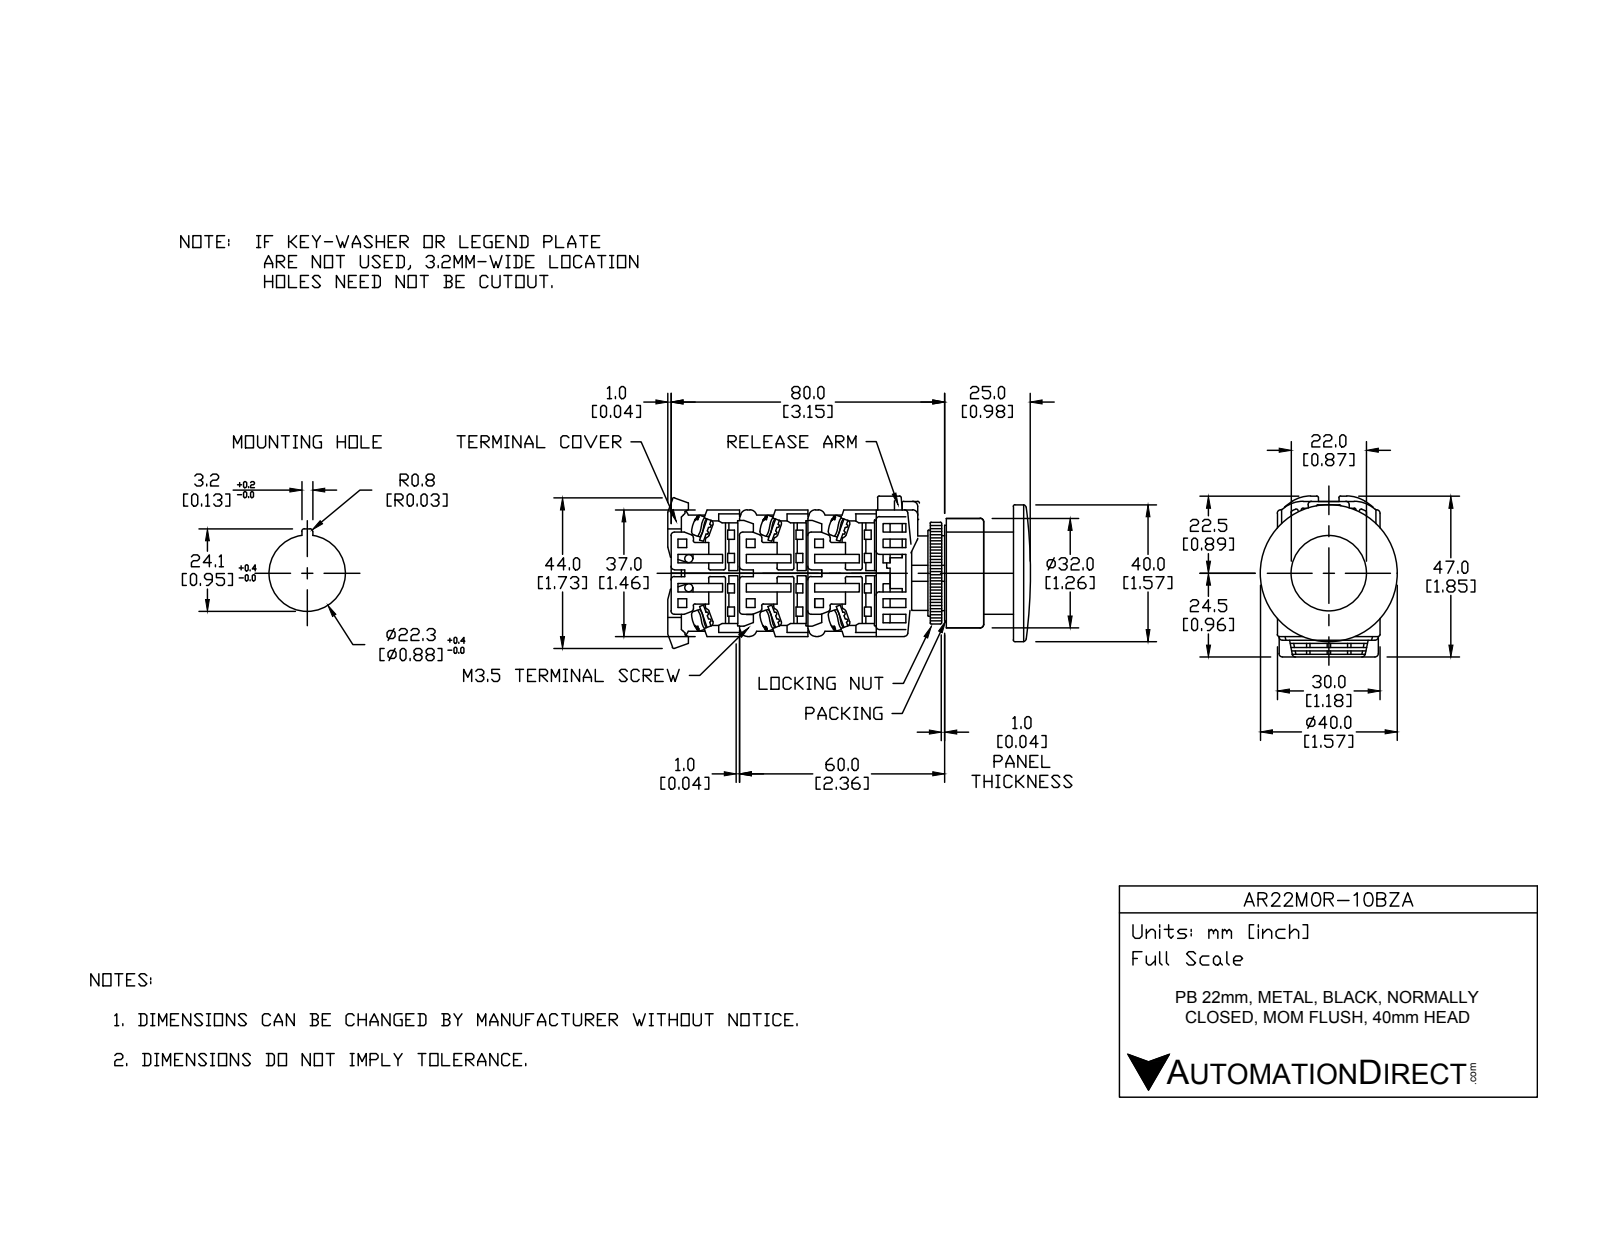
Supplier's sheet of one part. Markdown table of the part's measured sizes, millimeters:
| quantity | value |
| --- | --- |
| part name | AR22M0R-10BZA |
| STEP written by | SolidWorks 2017 (AUTOMOTIVE_DESIGN) |
| units | millimeters |
| bodies | 12 solids, 304 faces (202 planar, 76 cylindrical, 26 other) |
| overall size | 66.5 × 43 × 40 |
| volume | 37 326 mm³ |
| surface area | 22 079 mm² |
| round holes (diameter × count) | 21.8 × 1, 22 × 1, 25 × 1, 31 × 1 |
| round bosses / shafts (diameter × count) | 5 × 2, 40 × 1, 32 × 1, 30.5 × 1, 29.8 × 1, 24 × 1, 23.8 × 1, 21.75 × 1 |
| partial cylindrical surfaces (radius × count) | 0.5 × 23, 1.75 × 4, 5 × 4, 4 × 2, 16.59 × 1, 17.59 × 1 |
| main face-to-face distances | 1, 10, 28.5, 18, 38.5, 21, 3, 2, 29, 7.5 |
